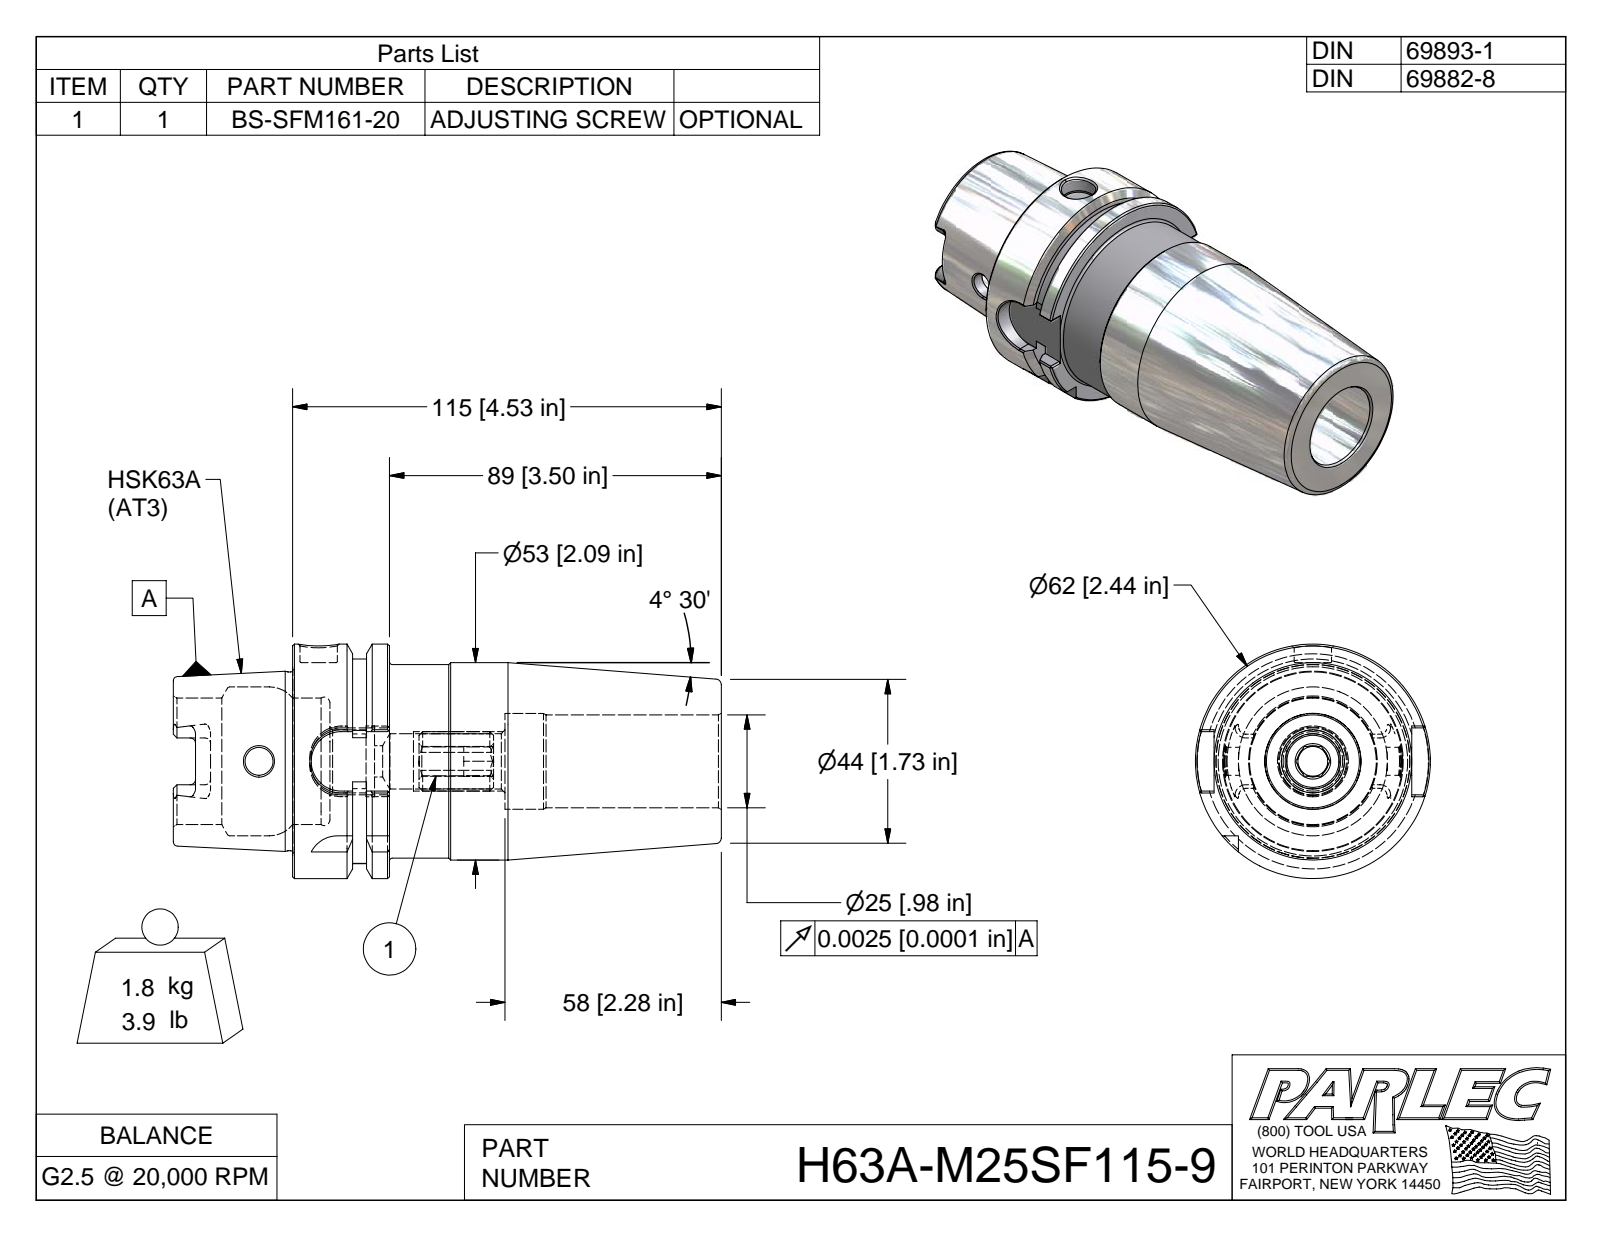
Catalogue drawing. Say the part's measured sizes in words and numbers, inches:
The part is named "H63A-M25SF115-9; H63A-M25SF115-9-1; BS-SFM161-20". Its 3-D file was written by "Autodesk Inventor 2009 (AUTOMOTIVE_DESIGN)". It is 2 solids with 168 faces: 66 planar, 37 cylindrical and 65 other. Overall it measures 5.787 by 2.48 by 2.48 inches. Its volume is 13.69 cubic inches and its surface area 67.44 square inches. Round holes: 1 of diameter 0.295, 1 of diameter 0.394, 1 of diameter 0.666, 1 of diameter 0.749, 1 of diameter 0.983, 1 of diameter 1.013, 1 of diameter 1.339, 1 of diameter 1.575. Round bosses or shafts: 1 of diameter 2.48, 1 of diameter 2.087, 1 of diameter 2.047, 1 of diameter 1.891. Partial cylindrical surfaces (rounded edges, fillets, slot ends): 6 of radius 0.059, 5 of radius 0.315, 4 of radius 0.113, 1 of radius 1.083. The main face-to-face distances are 3.504, 4.528, 1.024, 2.283, 0.241, 0.389, 0.394, 0.63, 4.134, 1.26.
